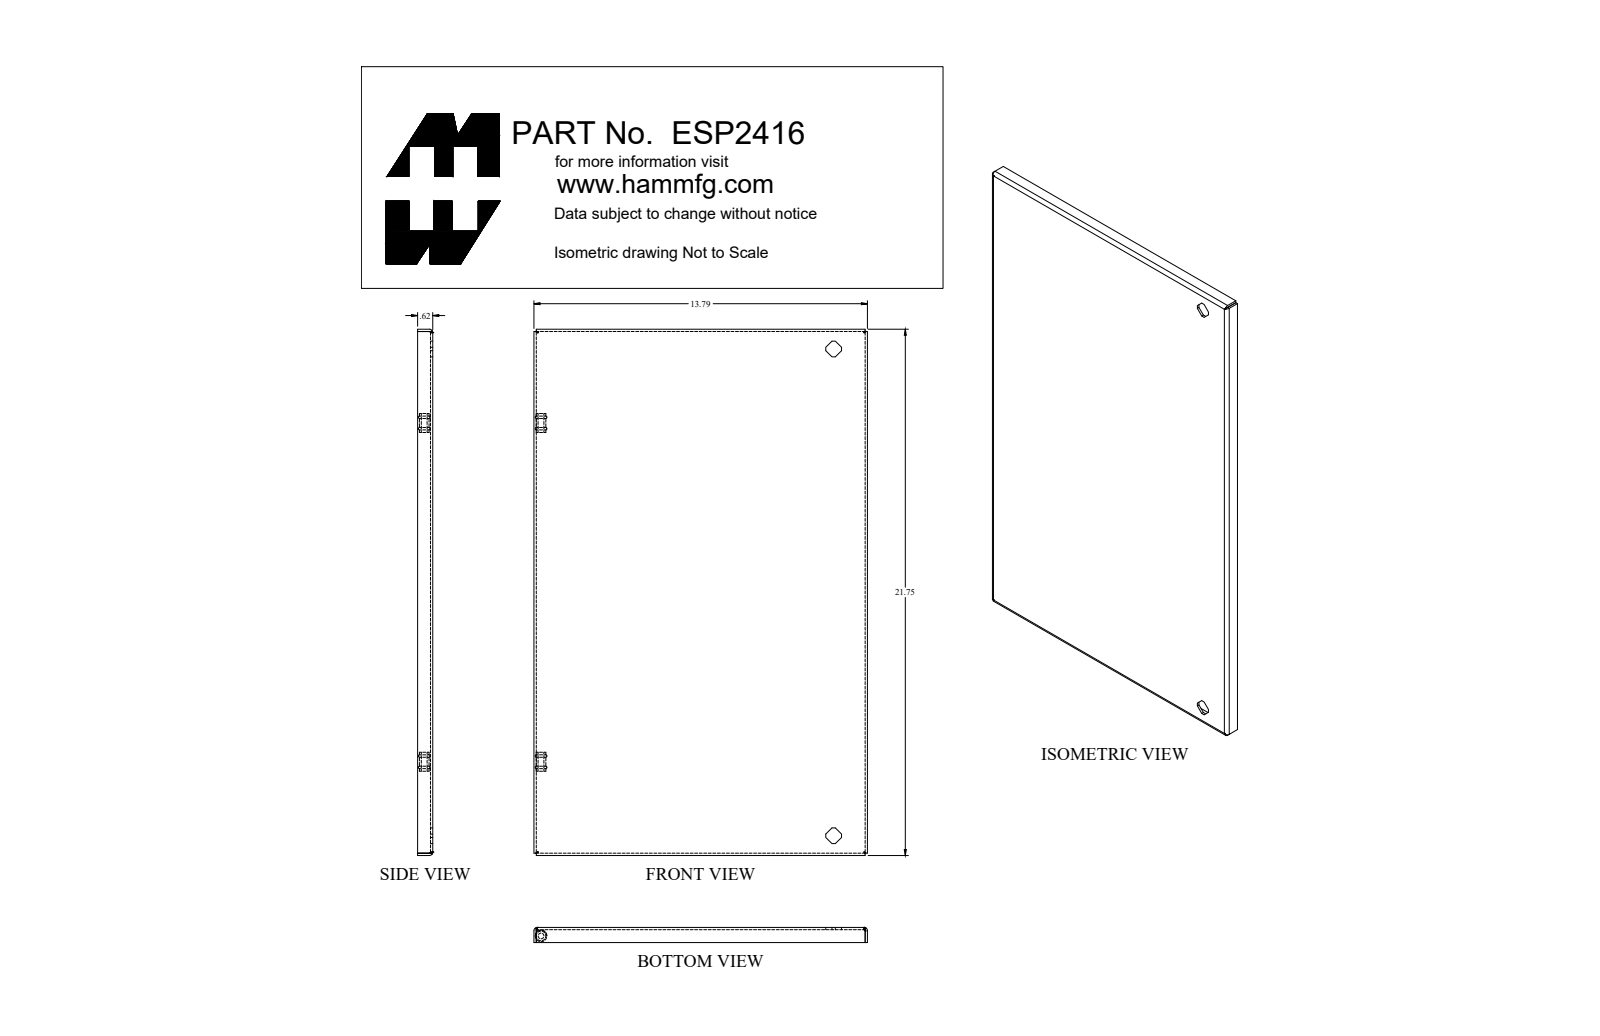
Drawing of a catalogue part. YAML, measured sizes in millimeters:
part_name: "ESP2416"
step_written_by: "SolidWorks 2018 (AUTOMOTIVE_DESIGN)"
units: millimeters
bodies: {solids: 13, faces: 584, planar: 354, cylindrical: 174, other: 56}
overall_size: [552.5, 398.9, 252.8]
volume: 766100
surface_area: 772900
round_holes:
  - {diameter: 3.5, count: 2}
  - {diameter: 6.1, count: 2}
  - {diameter: 13.1, count: 2}
round_bosses_or_shafts:
  - {diameter: 5.9, count: 6}
  - {diameter: 20, count: 2}
  - {diameter: 12.6, count: 2}
  - {diameter: 11, count: 2}
  - {diameter: 9, count: 2}
  - {diameter: 13.6, count: 1}
  - {diameter: 13.6, count: 1}
partial_cylinders:
  - {radius: 1.2, count: 28}
  - {radius: 0.3, count: 24}
  - {radius: 0.9, count: 6}
  - {radius: 2.7, count: 6}
  - {radius: 1.5, count: 4}
  - {radius: 3.6, count: 4}
  - {radius: 3.9, count: 4}
  - {radius: 4, count: 4}
face_to_face_distances: [2.4, 1.8, 355.8, 1, 20.7, 19.7, 19.7, 357.6, 509.6, 378.3]
hole_center_spacings: [355.6, 512]
